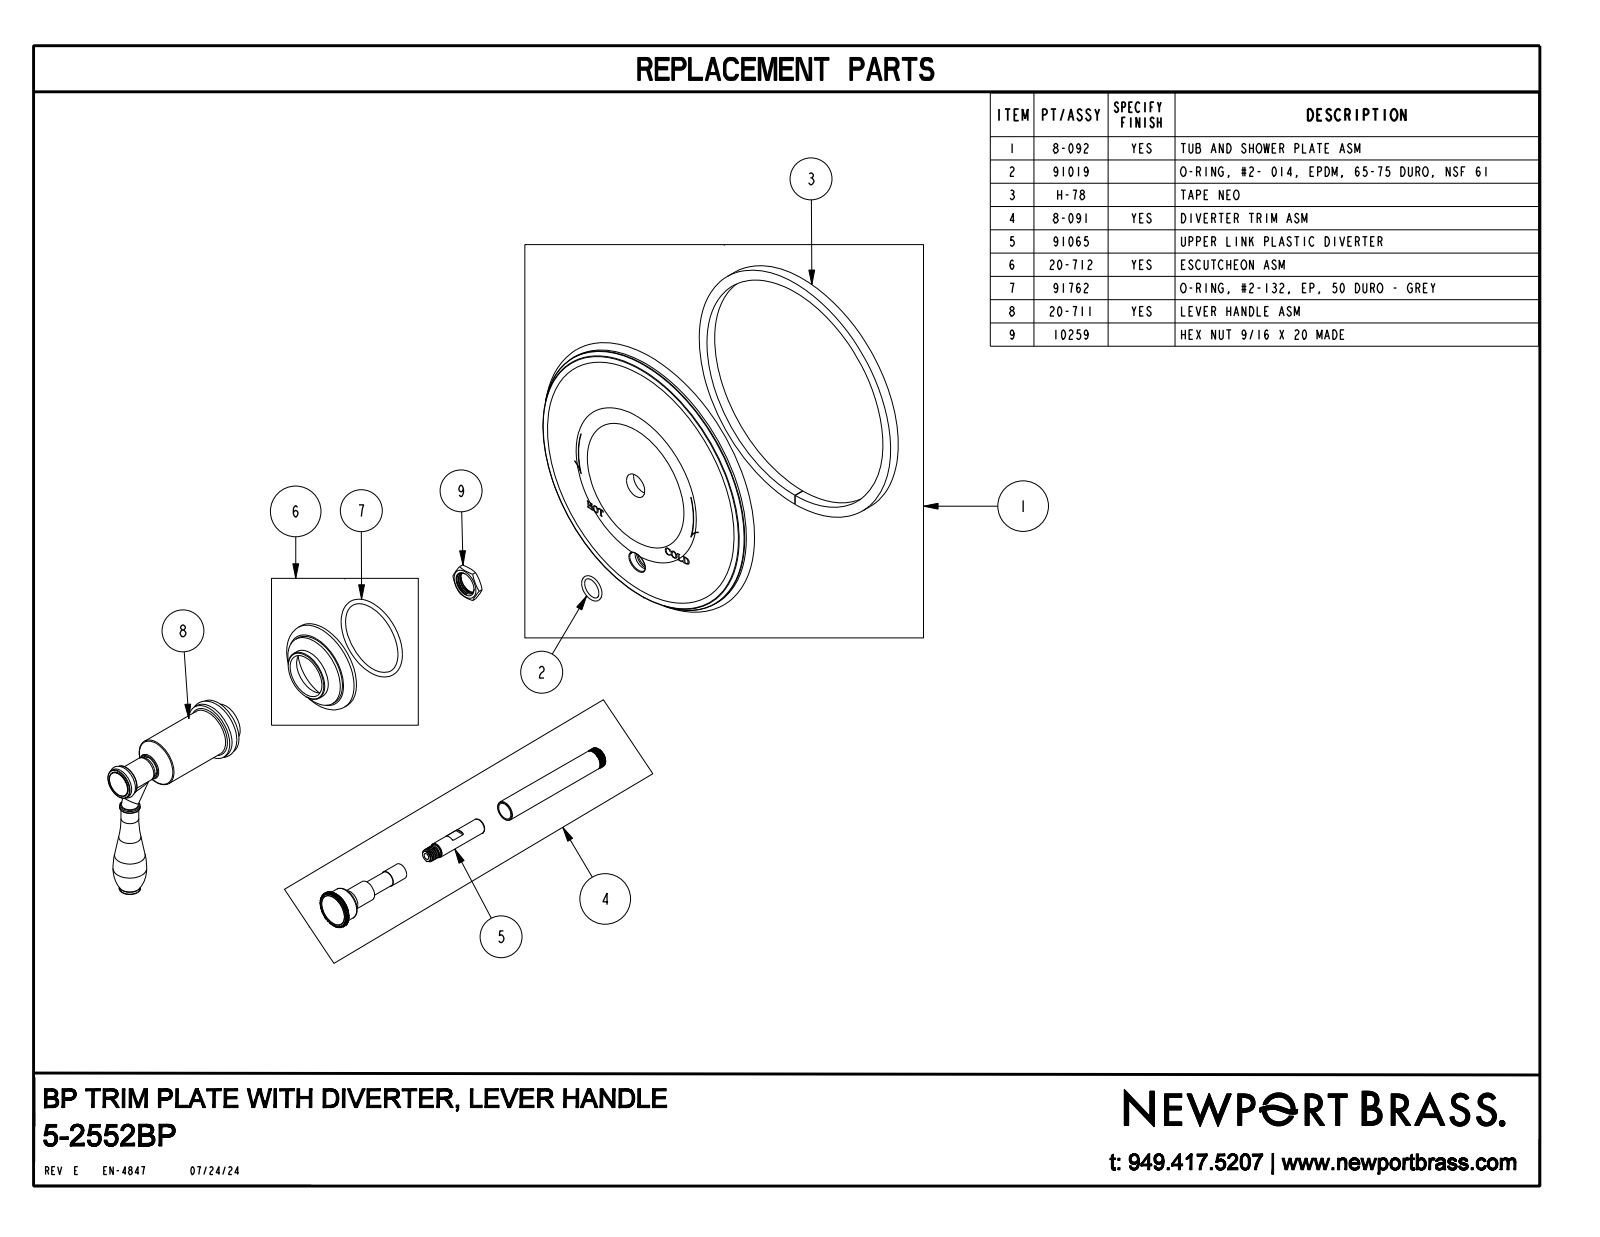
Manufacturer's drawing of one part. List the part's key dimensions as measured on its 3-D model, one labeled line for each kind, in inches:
Part name (STEP PRODUCT): 5-2552BP
STEP written by: CREO PARAMETRIC BY PTC INC, 2018400 (CONFIG_CONTROL_DESIGN)
Units: inches
Bodies: 1 solid, 682 faces (107 planar, 222 cylindrical, 353 other)
Overall size (bounding box): 6.75 × 6.75 × 4.241
Volume: 18.69 in³ · Surface area: 98.08 in²
Round holes (diameter × count): ⌀0.6 ×1
Round bosses / shafts (diameter × count): ⌀6.51 ×1, ⌀2.11 ×1, ⌀1.7 ×1, ⌀1.33 ×1, ⌀1.12 ×1, ⌀0.756 ×1, ⌀0.714 ×1, ⌀0.6 ×1
Partial cylindrical surfaces — rounded edges, fillets, slot ends (radius × count): R0.005 ×135, R0.435 ×1
Main face-to-face distances: 0.48, 0.313, 0.167, 0.93, 0.617, 0.45, 1.23, 0.917, 0.75, 0.3
